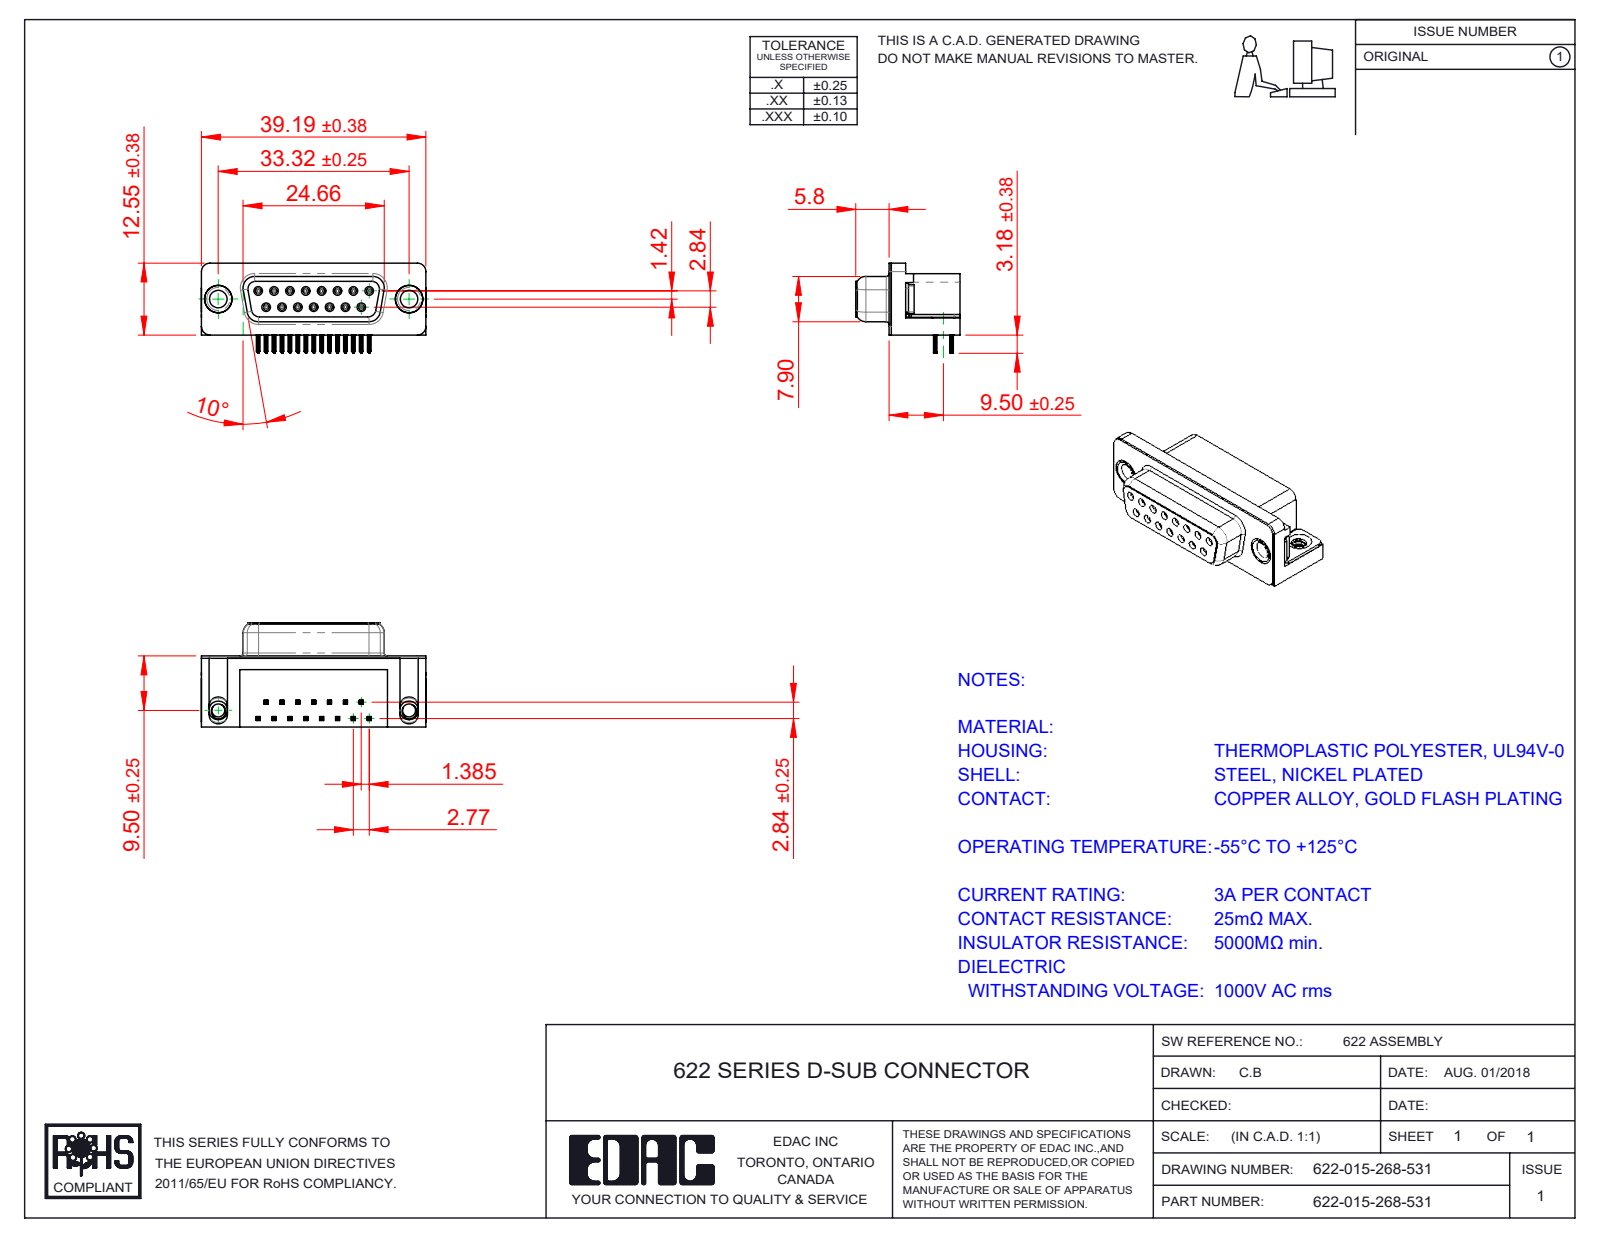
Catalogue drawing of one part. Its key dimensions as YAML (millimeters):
part_name: "622 Socket Bottom; 622 2 Prong Board Lock; 622 Housing_15 Socket; 622-015-268-531 (+3 more)"
step_written_by: "SolidWorks 2016 (CONFIG_CONTROL_DESIGN)"
units: millimeters
bodies: {solids: 21, faces: 2427, planar: 1106, cylindrical: 595, other: 726}
overall_size: [39.22, 18.2, 16.25]
volume: 5175
surface_area: 6698
round_holes:
  - {diameter: 0.8, count: 15}
  - {diameter: 0.9, count: 15}
  - {diameter: 3.05, count: 2}
  - {diameter: 4, count: 2}
  - {diameter: 4.8, count: 2}
  - {diameter: 5, count: 2}
round_bosses_or_shafts:
  - {diameter: 1.2, count: 15}
  - {diameter: 4.9, count: 2}
  - {diameter: 4.75, count: 2}
  - {diameter: 3.85, count: 2}
partial_cylinders:
  - {radius: 0.1, count: 120}
  - {radius: 0.15, count: 60}
  - {radius: 0.35, count: 30}
  - {radius: 1, count: 18}
  - {radius: 0.34, count: 15}
  - {radius: 0.5, count: 10}
  - {radius: 0.25, count: 8}
  - {radius: 1.35, count: 8}
face_to_face_distances: [0.4, 12, 6.2, 12.4, 10.35, 2.9, 0.85, 6.65, 0.35, 0.5]
hole_center_spacings: [3.16, 2.77, 5.54, 8.31, 11.08, 5.03, 5.04, 7.48]
